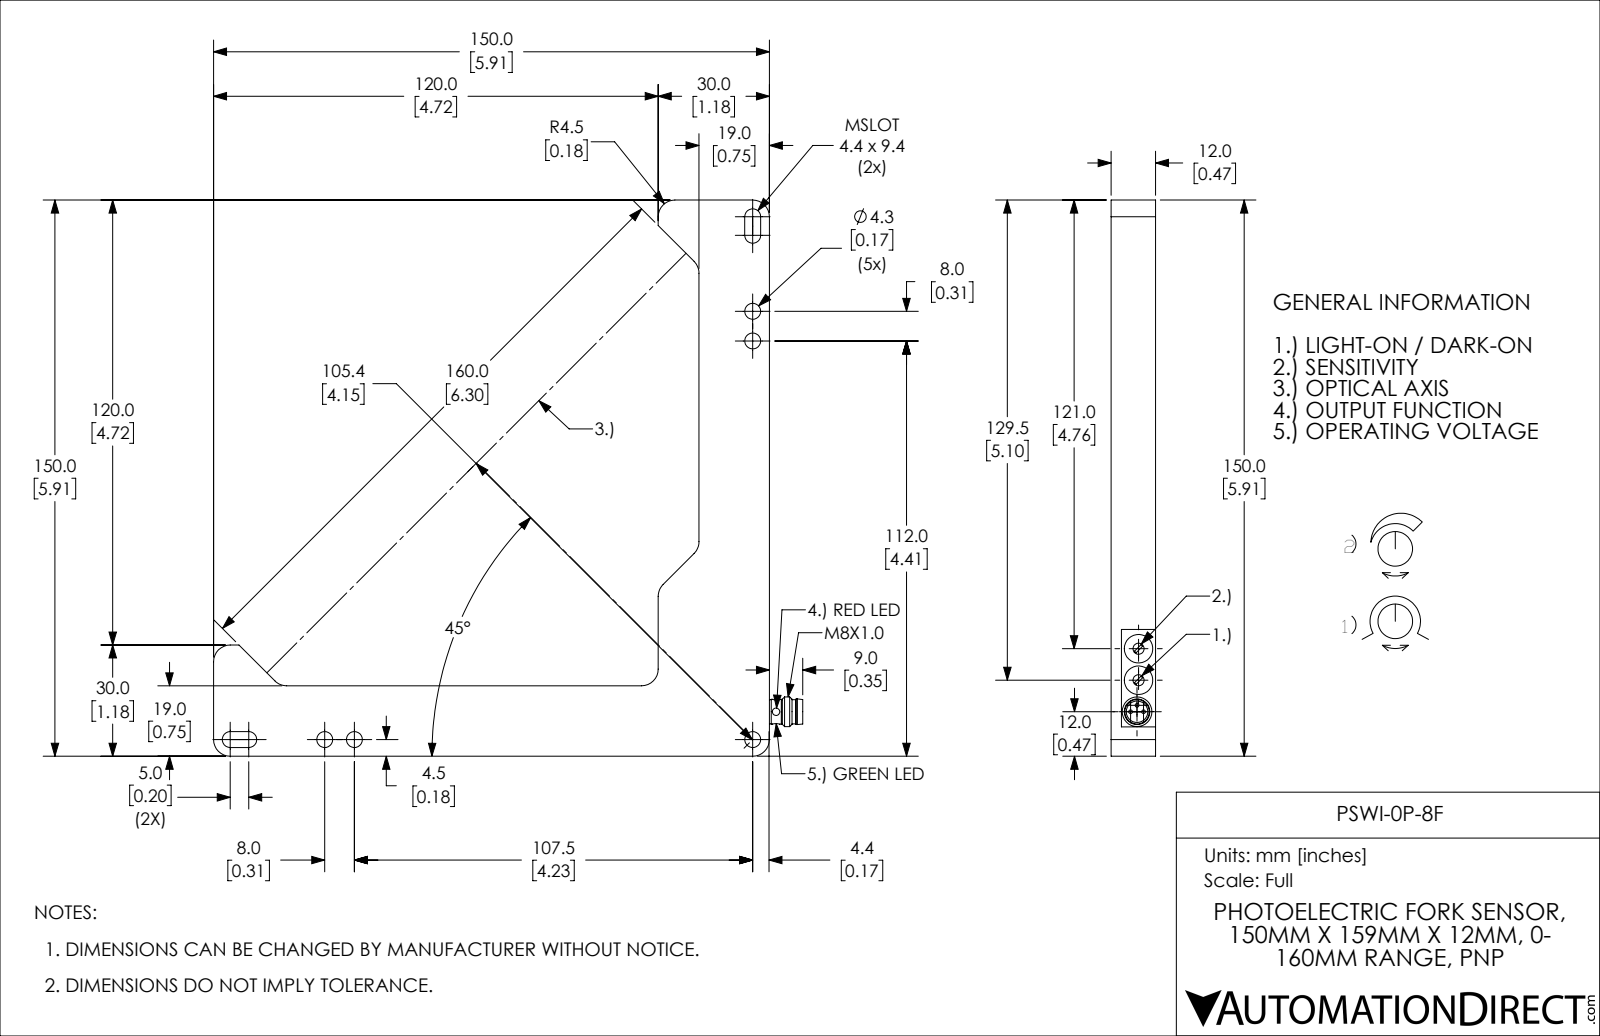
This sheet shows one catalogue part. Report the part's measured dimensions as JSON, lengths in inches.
{"part_name": "PSWI-0P-8F", "step_written_by": "SolidWorks 2017 (AUTOMOTIVE_DESIGN)", "units": "inches", "bodies": {"solids": 1, "faces": 90, "planar": 42, "cylindrical": 41, "other": 7}, "overall_size": [6.26, 5.906, 0.472], "volume_in3": 4.256, "surface_area_in2": 32.08, "round_holes": [[0.169, 5], [0.079, 2], [0.118, 2], [0.303, 2], [0.228, 1]], "round_bosses_or_shafts": [[0.039, 3], [0.315, 1], [0.272, 1], [0.264, 1], [0.257, 1]], "partial_cylinders_radius": [[0.177, 10], [0.085, 4], [0.049, 2]], "face_to_face_distances": [0.472, 0.748, 5.906, 5.157, 1.181, 0.433, 4.724, 6.298, 0.093, 0.262], "hole_center_spacings": [0.315, 4.232, 4.547, 6.212, 0.335, 0.335, 0.385, 0.669]}
